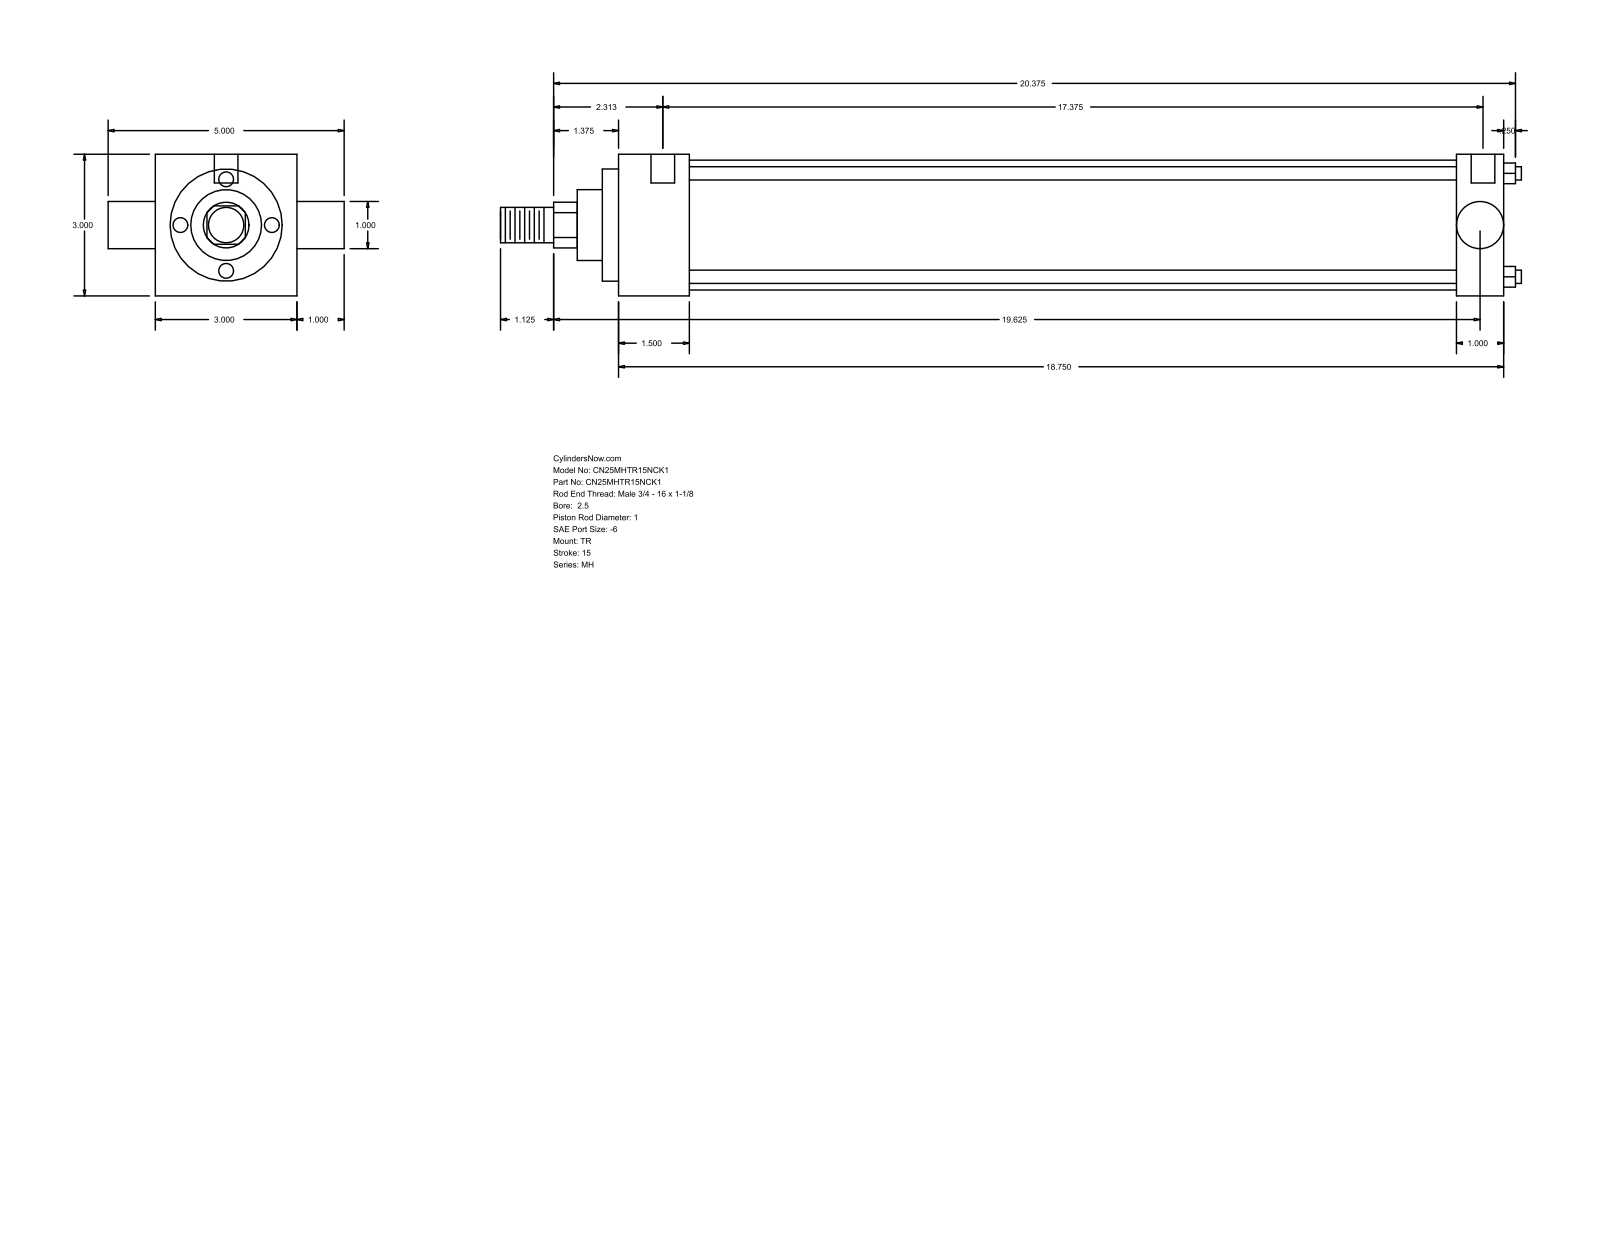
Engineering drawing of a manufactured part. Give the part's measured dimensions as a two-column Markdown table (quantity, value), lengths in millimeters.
| quantity | value |
| --- | --- |
| part name | MH_TR__0250_1 |
| STEP written by | GSSL Pune (CONFIG_CONTROL_DESIGN) |
| units | millimeters |
| bodies | 0 solids, 86 faces (61 planar, 25 cylindrical, 0 other) |
| overall size | 549.27 × 127 × 76.2 |
| round holes (diameter × count) | 5.56 × 3, 12.7 × 2 |
| round bosses / shafts (diameter × count) | 7.14 × 4, 69.85 × 1, 60.33 × 1, 38.1 × 1, 25.4 × 1, 25.35 × 1, 19.05 × 1 |
| partial cylindrical surfaces (radius × count) | 12.29 × 1 |
| main face-to-face distances | 76.2, 476.26, 38.11, 438.15, 450.85, 412.74, 25.41, 8.73, 46.84, 459.58 |
| hole center spacings | 3.18, 4.76, 441.32, 444.5, 446.08, 449.26 |
